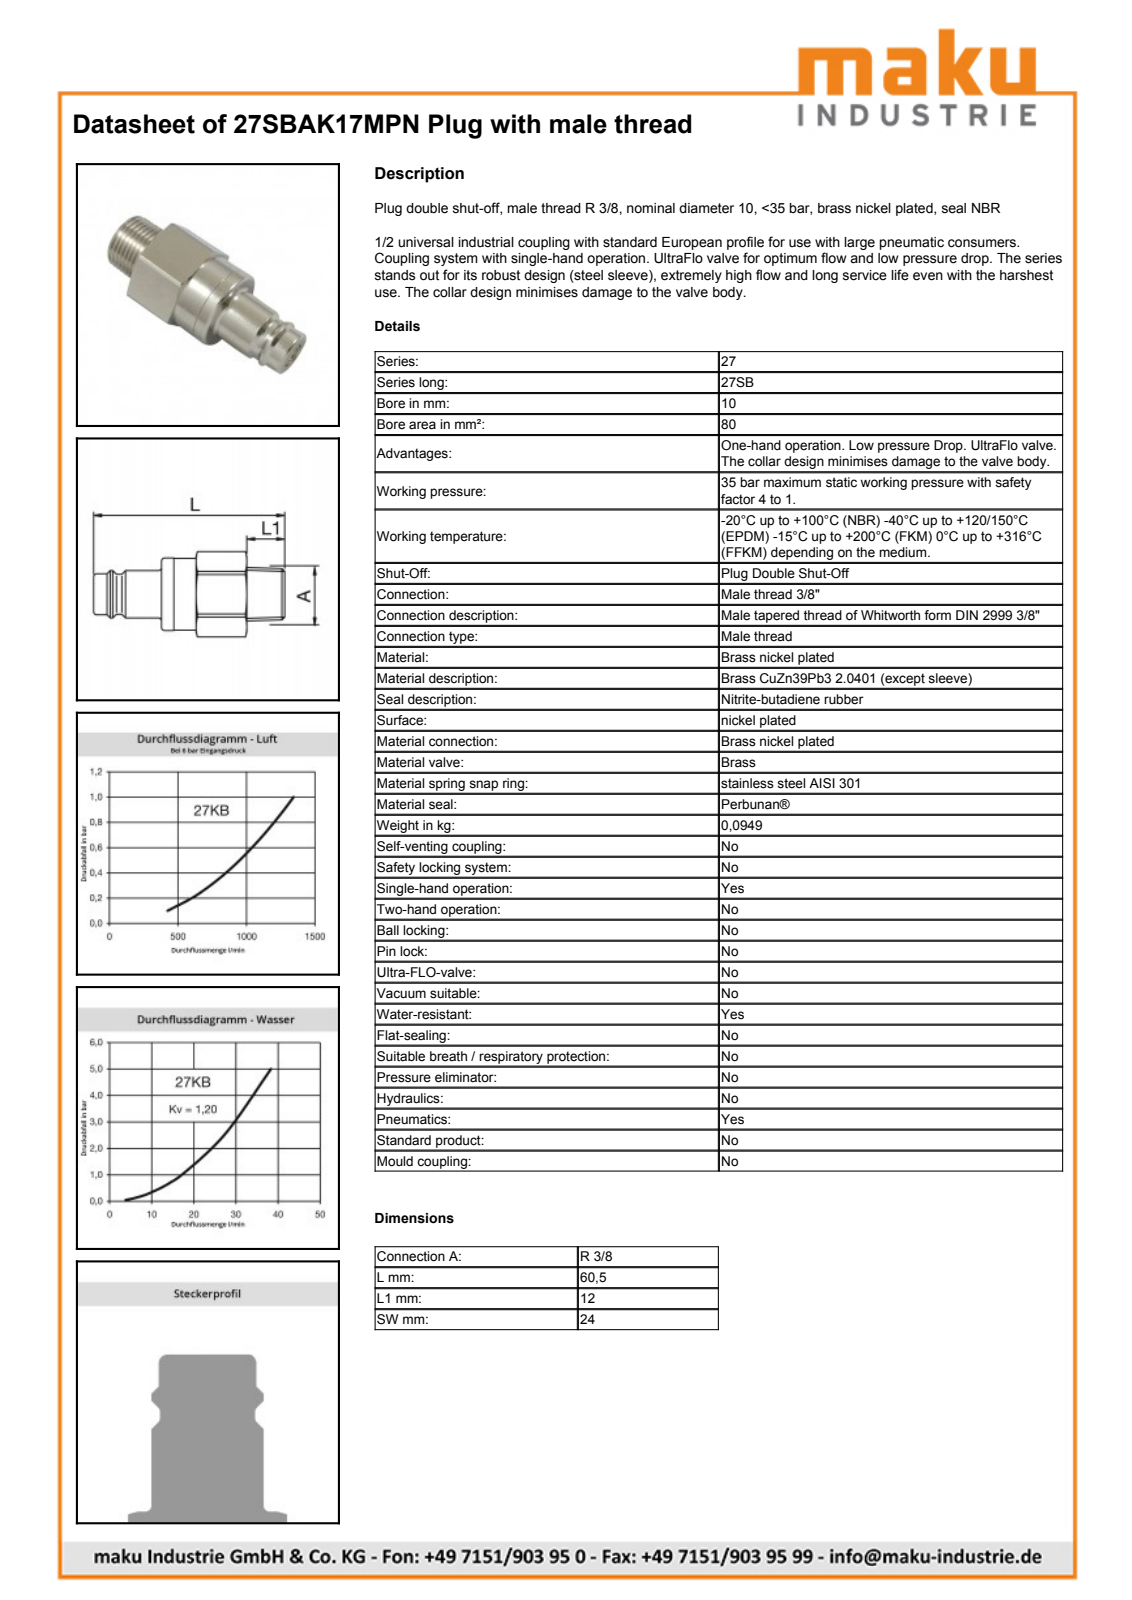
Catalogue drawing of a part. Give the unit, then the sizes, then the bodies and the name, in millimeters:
Units: millimetres
Overall size (bounding box): 60.5 × 26.69 × 26.06
Round holes (diameter × count): ⌀12.1 ×1, ⌀18 ×1, ⌀19 ×1, ⌀20.3 ×1
Round bosses / shafts (diameter × count): ⌀23 ×1, ⌀22.75 ×1, ⌀18.5 ×1, ⌀15 ×1, ⌀13 ×1, ⌀12.65 ×1
Partial cylindrical surfaces — rounded edges, fillets, slot ends (radius × count): R13.53 ×1
Main face-to-face distances: 24, 24.02, 12, 27, 39, 21.5, 48.5, 60.5, 25.4, 3.9
Volume: 15 611 mm³ · Surface area: 8 131 mm²
Bodies: 1 solid, 80 faces (33 planar, 19 cylindrical, 28 other)
Part name (STEP PRODUCT): D107537
STEP written by: Autodesk Inventor 2013 (AUTOMOTIVE_DESIGN)
